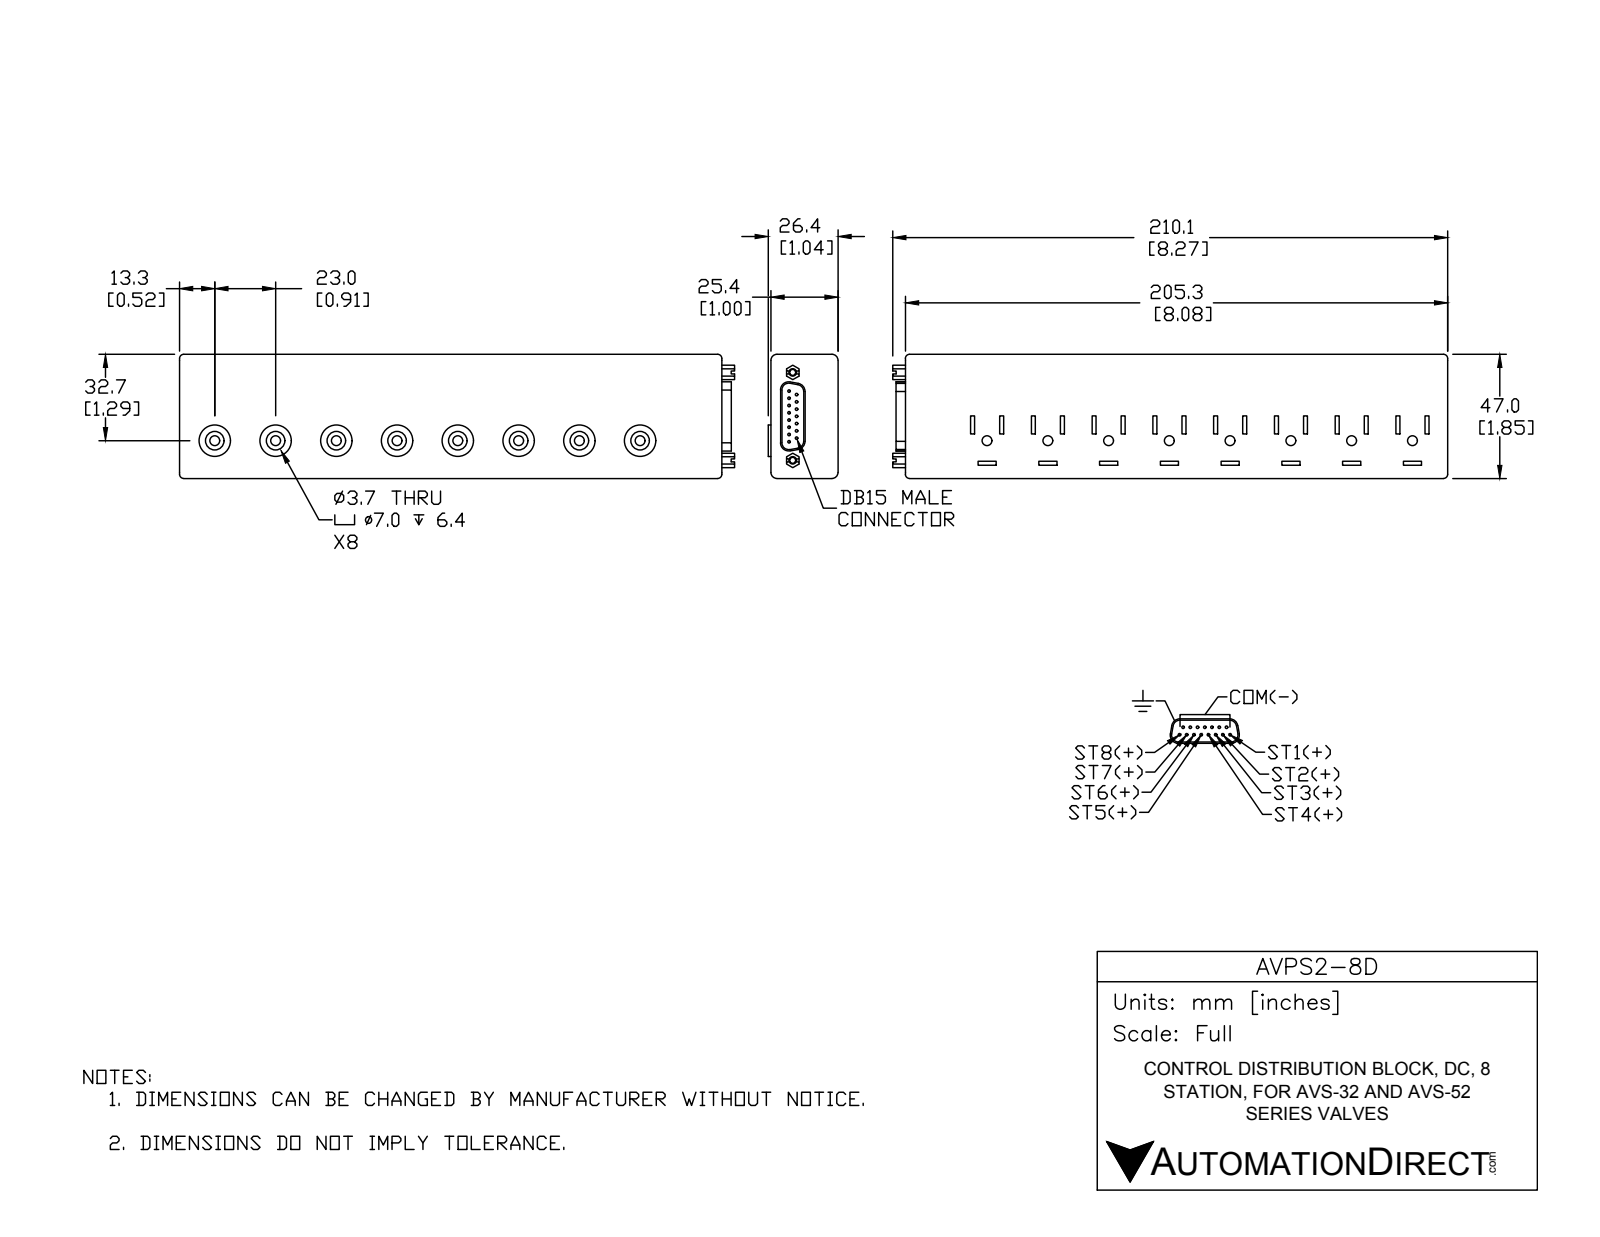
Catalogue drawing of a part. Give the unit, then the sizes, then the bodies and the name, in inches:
Units: inches
Overall size (bounding box): 8.273 × 1.85 × 1.04
Round holes (diameter × count): ⌀0.145 ×8, ⌀0.275 ×8, ⌀0.089 ×2
Round bosses / shafts (diameter × count): ⌀0.039 ×15, ⌀0.469 ×8
Partial cylindrical surfaces — rounded edges, fillets, slot ends (radius × count): R0.062 ×8, R0.09 ×4, R0.102 ×4, R0.122 ×4
Main face-to-face distances: 1, 1.85, 8.084, 0.04, 1.04, 0.059, 0.25, 0.79, 0.906, 1.812
Hole centre spacings: 0.906, 1.812, 2.718, 3.624, 0.906, 1.812, 4.53, 5.436
Volume: 14.61 in³ · Surface area: 58.73 in²
Bodies: 1 solid, 311 faces (195 planar, 104 cylindrical, 12 other)
Part name (STEP PRODUCT): AVPS2-8D
STEP written by: SolidWorks 2016 (AUTOMOTIVE_DESIGN)
